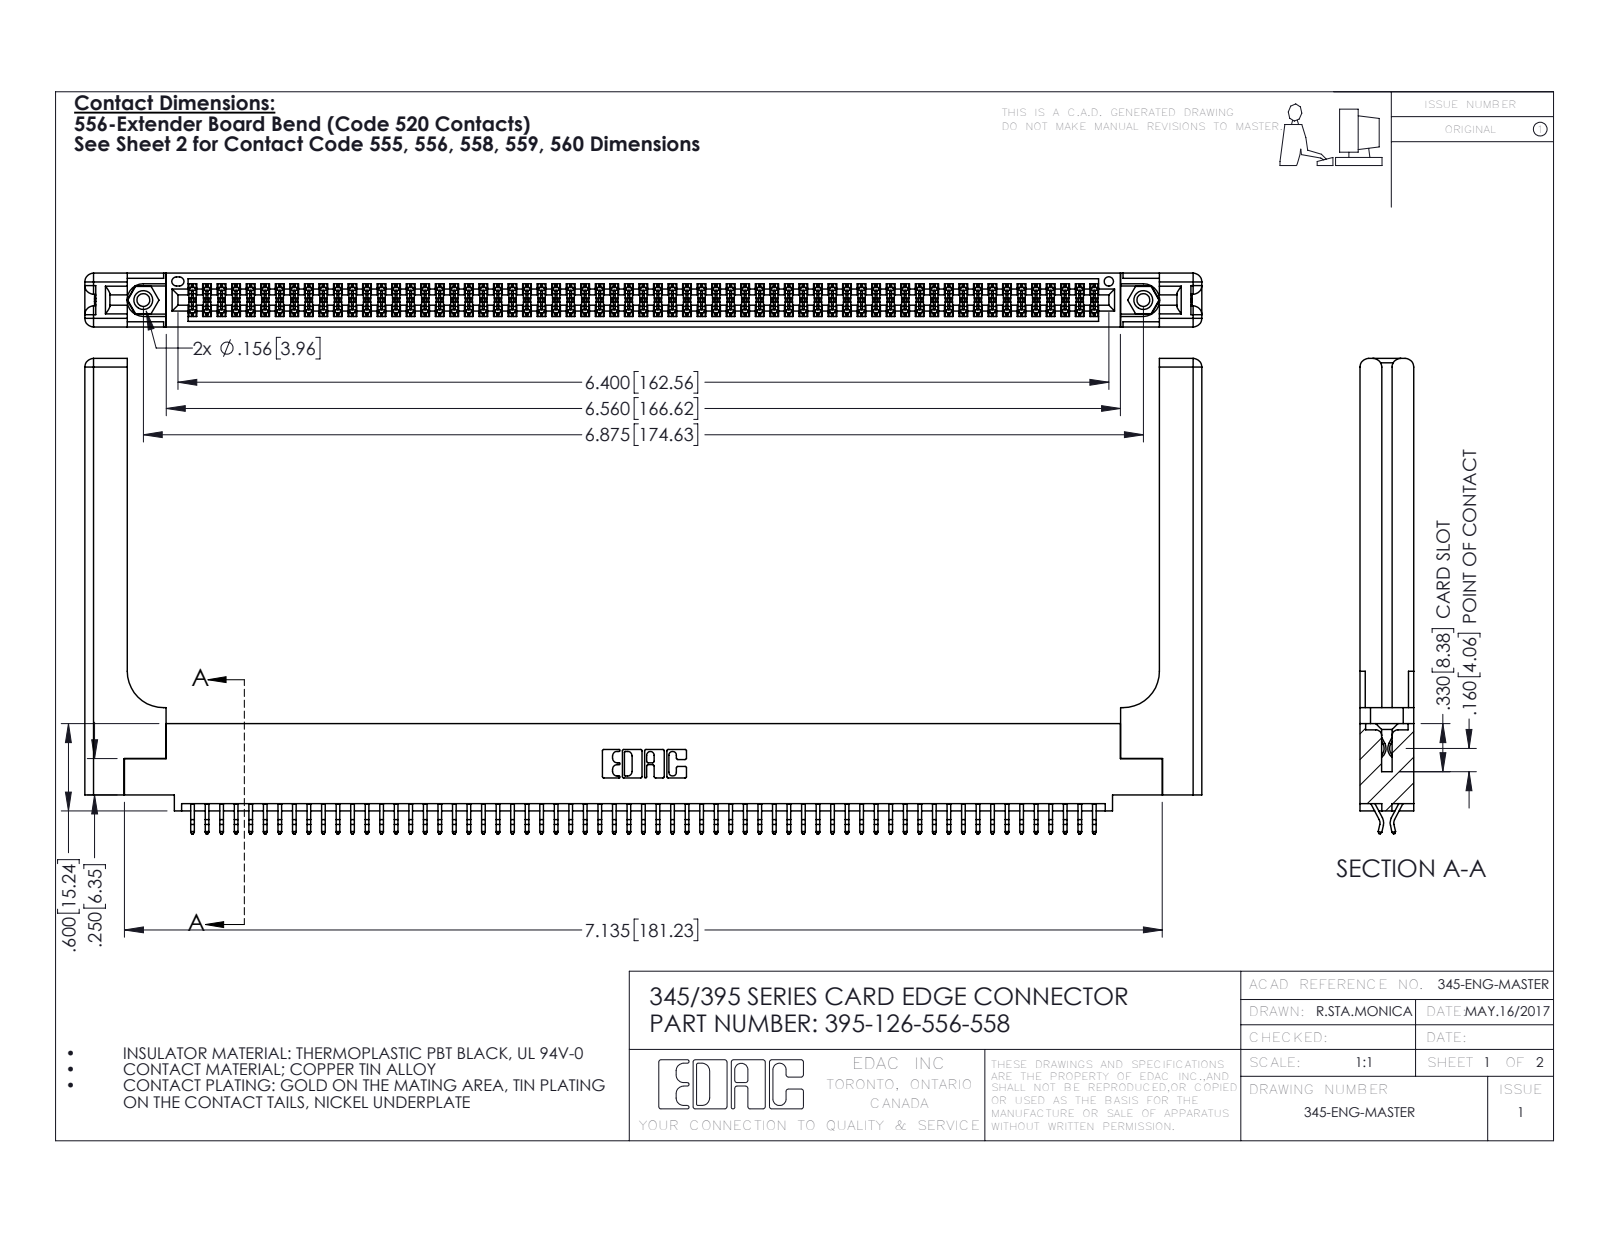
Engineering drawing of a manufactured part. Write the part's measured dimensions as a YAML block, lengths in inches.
part_name: "345-292-001_556 Tail; 345-220-058_345-220-058; 395-126-556-558; 345-250-001_345-250-001-102 (+1 more)"
step_written_by: "SolidWorks 2016 (CONFIG_CONTROL_DESIGN)"
units: inches
bodies: {solids: 131, faces: 7442, planar: 4894, cylindrical: 2488, other: 60}
overall_size: [7.679, 3.267, 0.37]
volume: 1.681
surface_area: 52.12
round_holes:
  - {diameter: 0.089, count: 2}
  - {diameter: 0.125, count: 2}
  - {diameter: 0.156, count: 2}
  - {diameter: 0.064, count: 1}
round_bosses_or_shafts:
  - {diameter: 0.155, count: 2}
partial_cylinders:
  - {radius: 0.006, count: 189}
  - {radius: 0.01, count: 22}
  - {radius: 0.06, count: 16}
  - {radius: 0.007, count: 6}
  - {radius: 0.031, count: 6}
  - {radius: 0.026, count: 3}
  - {radius: 0.01, count: 2}
  - {radius: 0.014, count: 2}
face_to_face_distances: [0.072, 0.298, 0.37, 0.025, 0.098, 0.272, 0.2, 0.225, 0.148, 0.15]
hole_center_spacings: [0.27, 6.639, 6.875]
